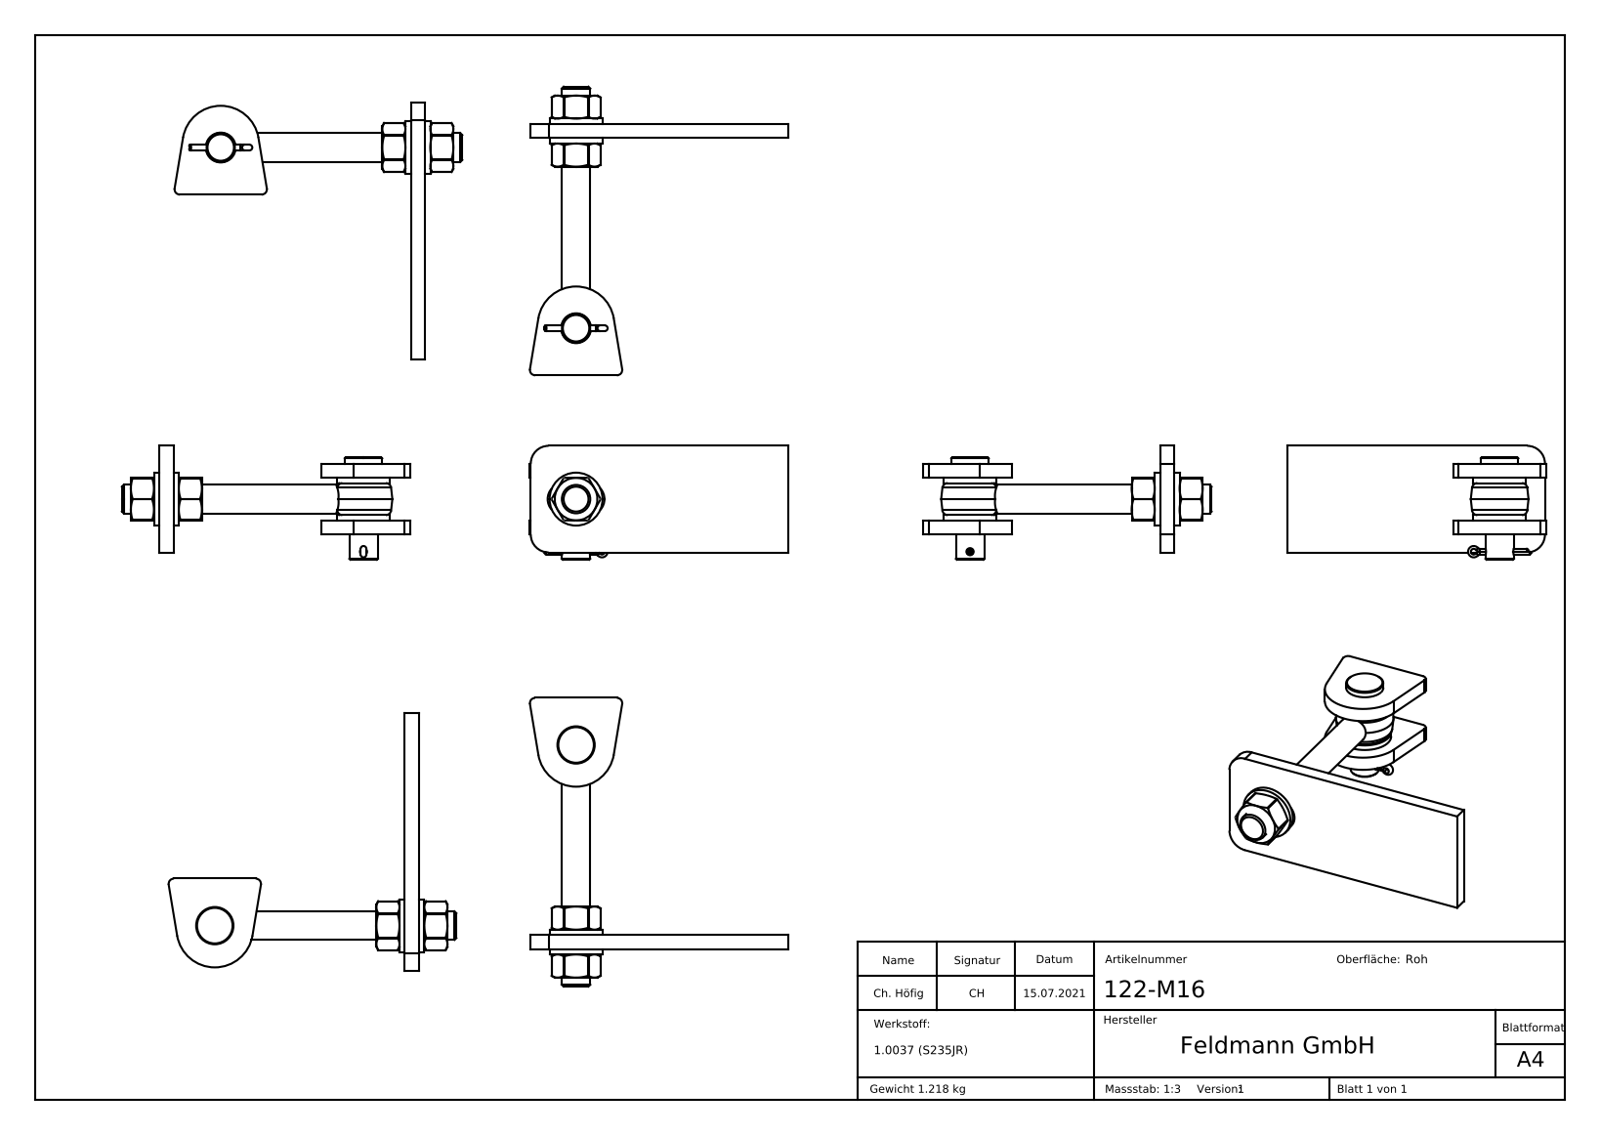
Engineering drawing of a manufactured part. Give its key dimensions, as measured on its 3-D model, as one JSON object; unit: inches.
{"part_name": "Splint DIN94 - ISO 1234 Konfig; Splint DIN94 - ISO 1234 Konfig_DIN 94 3,2x30; DIN 934 M4-M20; Torband Teil1 (+8 more)", "step_written_by": "SolidWorks 2018 (CONFIG_CONTROL_DESIGN)", "units": "inches", "bodies": {"solids": 12, "faces": 404, "planar": 176, "cylindrical": 85, "other": 143}, "overall_size": [944.882, 551.181, 551.181], "volume_in3": 9.518, "surface_area_in2": 85.84, "round_holes": [[0.669, 2], [0.157, 1], [0.551, 1], [0.646, 1], [0.661, 1]], "round_bosses_or_shafts": [[1.173, 2], [0.827, 1], [0.63, 1], [0.626, 1], [0.126, 1]], "partial_cylinders_radius": [[0.02, 6], [0.039, 2], [0.102, 2], [0.118, 2], [0.354, 2], [0.394, 2], [0.063, 1], [0.327, 1]], "face_to_face_distances": [0.315, 1.26, 0.945, 0.827, 0.433, 0.118, 0.709, 0.394, 1.654, 1.969]}
